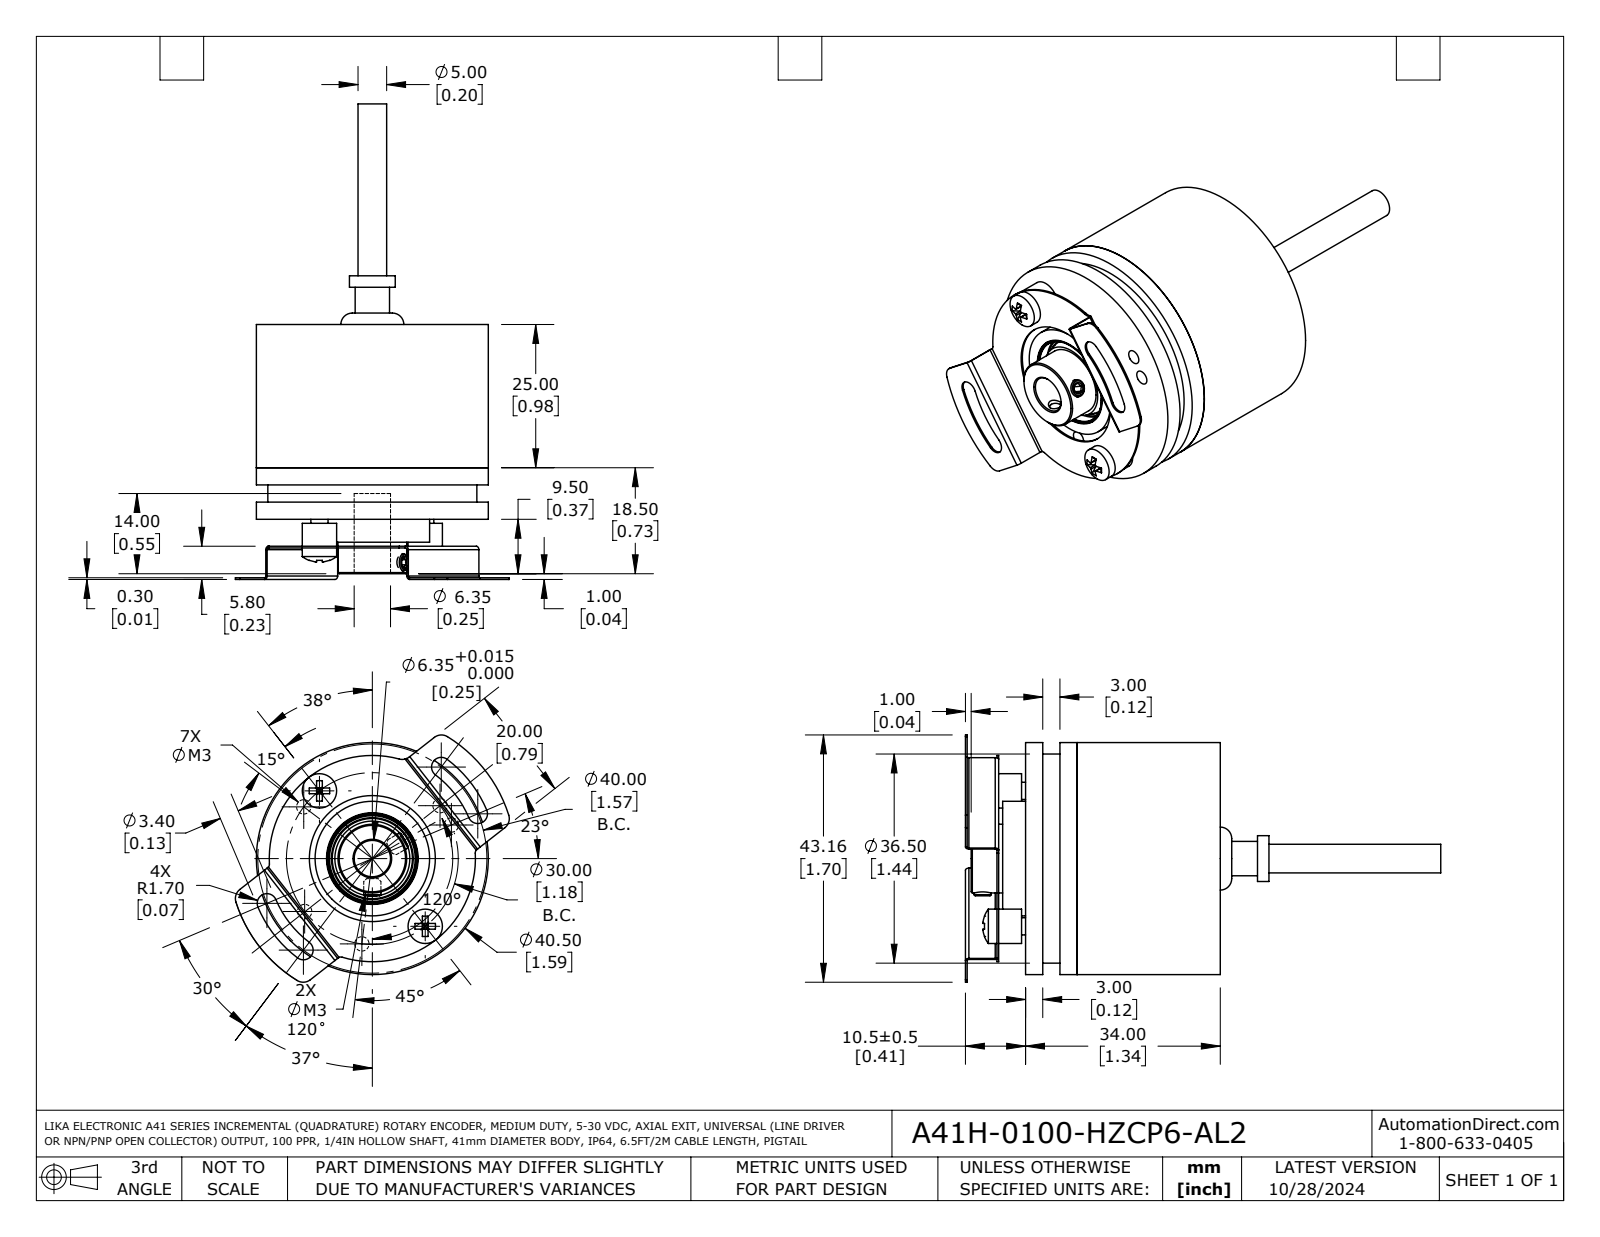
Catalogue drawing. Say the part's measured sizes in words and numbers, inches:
The part is named "A41H-0100-HZCP6-AL2". Its 3-D file was written by "SolidWorks 2021 (AUTOMOTIVE_DESIGN)". It is 15 solids with 465 faces: 139 planar, 186 cylindrical and 140 other. Overall it measures 3.268 by 1.883 by 1.699 inches. Its volume is 1.187 cubic inches and its surface area 32.38 square inches. Round holes: 9 of diameter 0.098, 7 of diameter 0.063, 3 of diameter 0.157, 2 of diameter 0.087, 2 of diameter 0.126, 2 of diameter 0.138, 1 of diameter 0.169, 1 of diameter 0.25, 1 of diameter 0.295, 1 of diameter 0.512, 1 of diameter 0.602, 1 of diameter 0.612. Round bosses or shafts: 4 of diameter 0.118, 3 of diameter 0.236, 2 of diameter 0.15, 2 of diameter 0.079, 1 of diameter 1.594, 1 of diameter 1.496, 1 of diameter 1.457, 1 of diameter 1.437. Partial cylindrical surfaces (rounded edges, fillets, slot ends): 14 of radius 0.039, 8 of radius 0.008, 5 of radius 0.079, 4 of radius 0.012, 4 of radius 0.024, 4 of radius 0.067, 3 of radius 0.03, 1 of radius 0.709. The main face-to-face distances are 0.118, 0.433, 1.339, 0.906, 0.197, 1.22, 0.079, 0.866, 0.039, 0.787. The hole center spacings are 0.591, 0.669, 0.835, 0.11, 0.118, 0.837, 0.945, 1.023.
